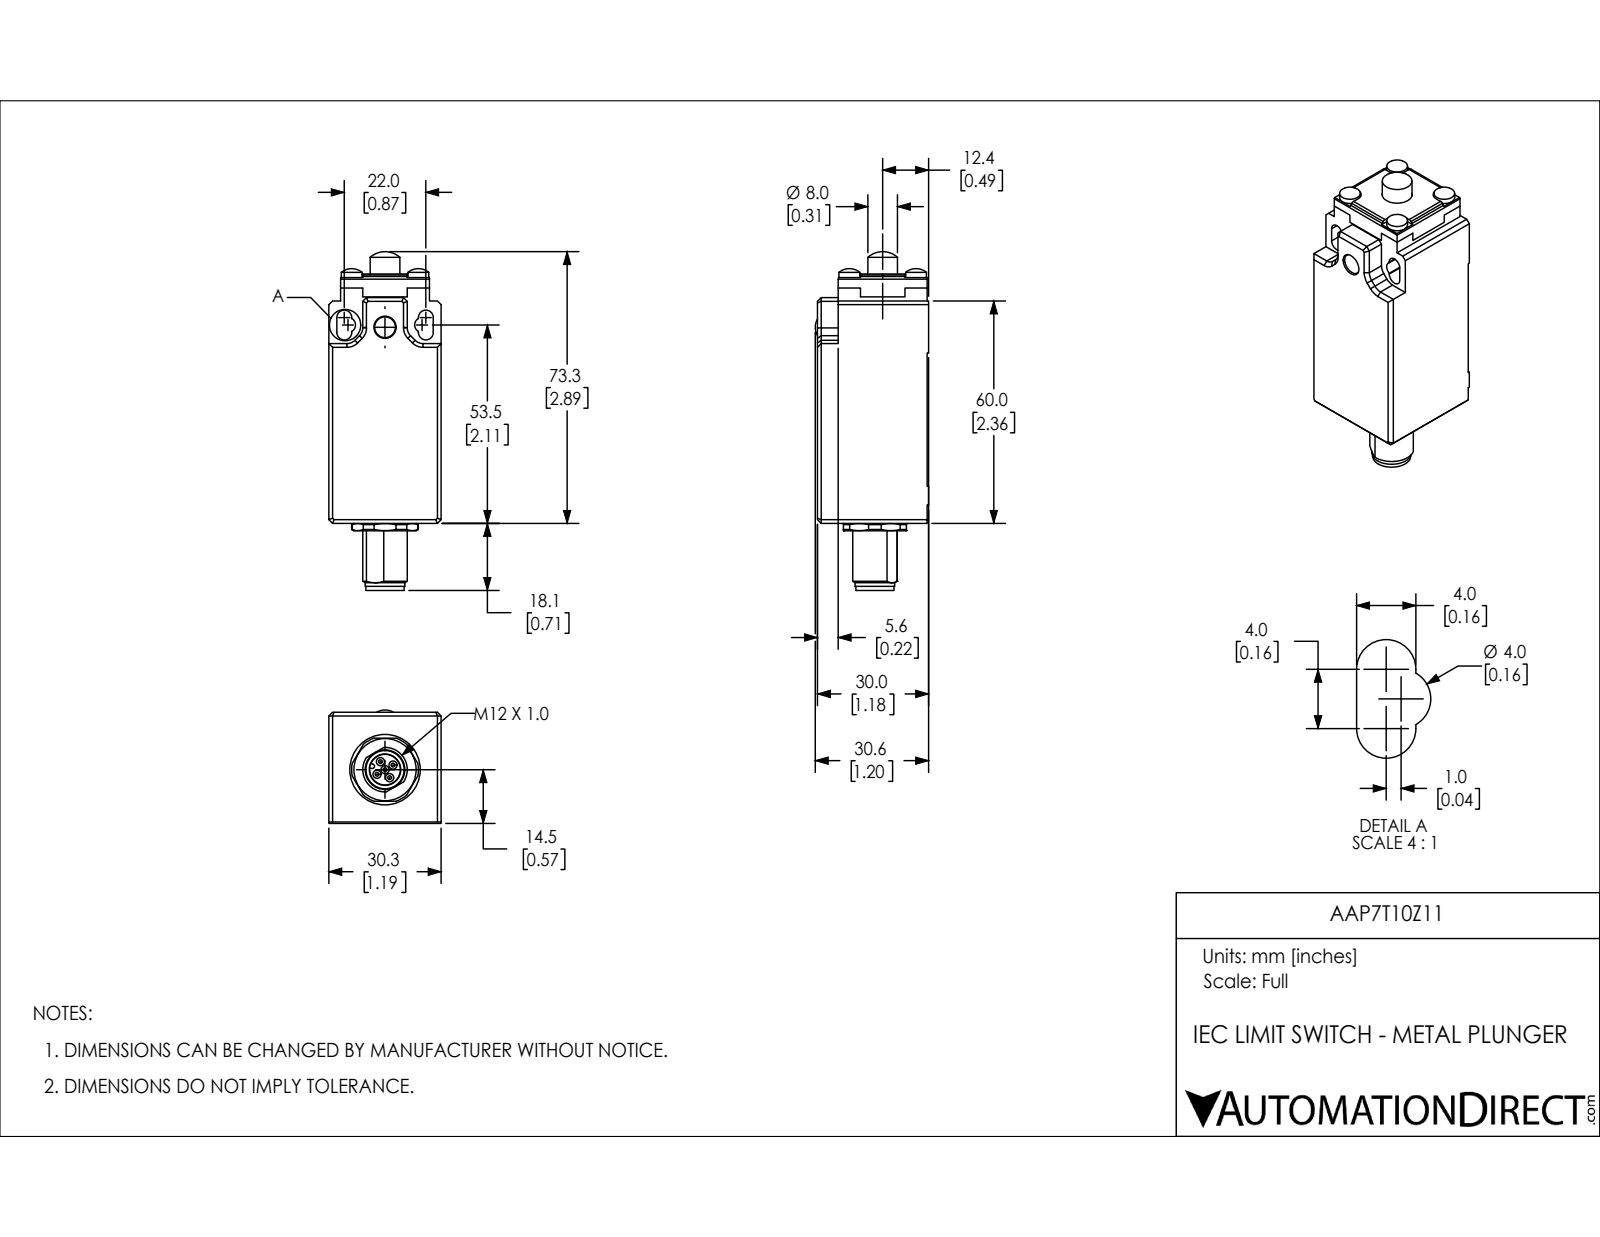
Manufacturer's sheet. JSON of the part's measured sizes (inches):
{"part_name": "AAP7T10Z11", "step_written_by": "SolidWorks 2018 (AUTOMOTIVE_DESIGN)", "units": "inches", "bodies": {"solids": 4, "faces": 293, "planar": 134, "cylindrical": 112, "other": 47}, "overall_size": [3.598, 1.205, 1.193], "volume_in3": 3.543, "surface_area_in2": 23.43, "round_holes": [[0.087, 5], [0.236, 1], [0.319, 1], [0.512, 1], [0.551, 1], [0.63, 1]], "round_bosses_or_shafts": [[0.22, 5], [0.055, 5], [0.039, 5], [0.421, 1], [0.406, 1], [0.315, 1]], "partial_cylinders_radius": [[0.039, 8], [0.118, 8], [0.079, 6], [0.024, 1], [0.236, 1], [0.354, 1], [0.394, 1], [0.4, 1]], "face_to_face_distances": [1.193, 1.165, 2.406, 0.016, 1.181, 0.945, 0.236, 0.039, 2.65, 0.244], "hole_center_spacings": [0.098, 0.139, 0.197, 0.041, 0.083, 0.099, 0.139, 0.152]}
